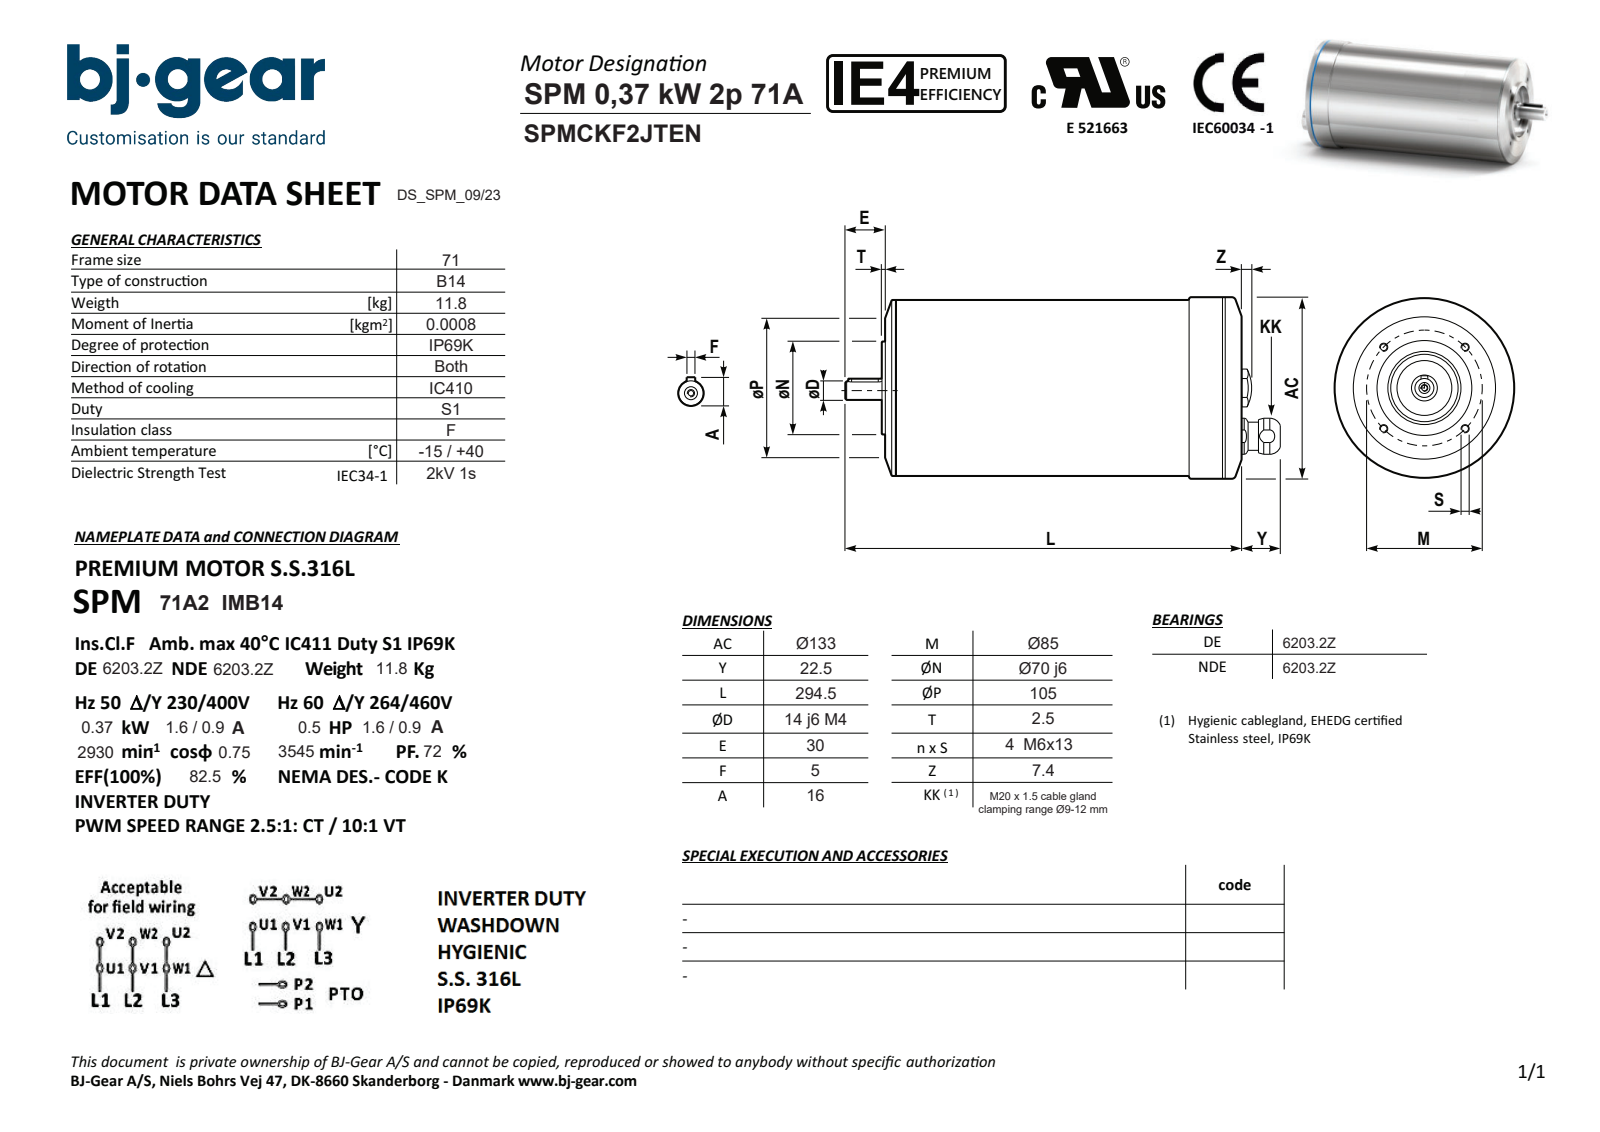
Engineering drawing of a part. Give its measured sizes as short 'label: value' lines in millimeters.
name: SPMCKF2JTENN4KSA1-N---NNN
written by: Solid Edge (AUTOMOTIVE_DESIGN)
unit: mm
bodies: 1 solid, 90 faces (31 planar, 33 cylindrical, 26 other)
size: 322 × 133 × 133
volume: 3 471 000 mm³; area: 138 275 mm²
holes: 4× ⌀4.92, 1× ⌀4.13, 1× ⌀5.3, 1× ⌀7, 1× ⌀13.4, 1× ⌀52, 1× ⌀62
bosses: 1× ⌀133, 1× ⌀132.98, 1× ⌀129, 1× ⌀128.98, 1× ⌀70, 1× ⌀20, 1× ⌀17, 1× ⌀14
rounds: 2× R2.5, 1× R12.8
face distances: 264.5, 259, 5.5, 263.5, 4.5, 1, 2.5, 8, 267, 3.5
hole spacings: 42.5, 60.1, 30.31, 70.75, 84.99, 34
